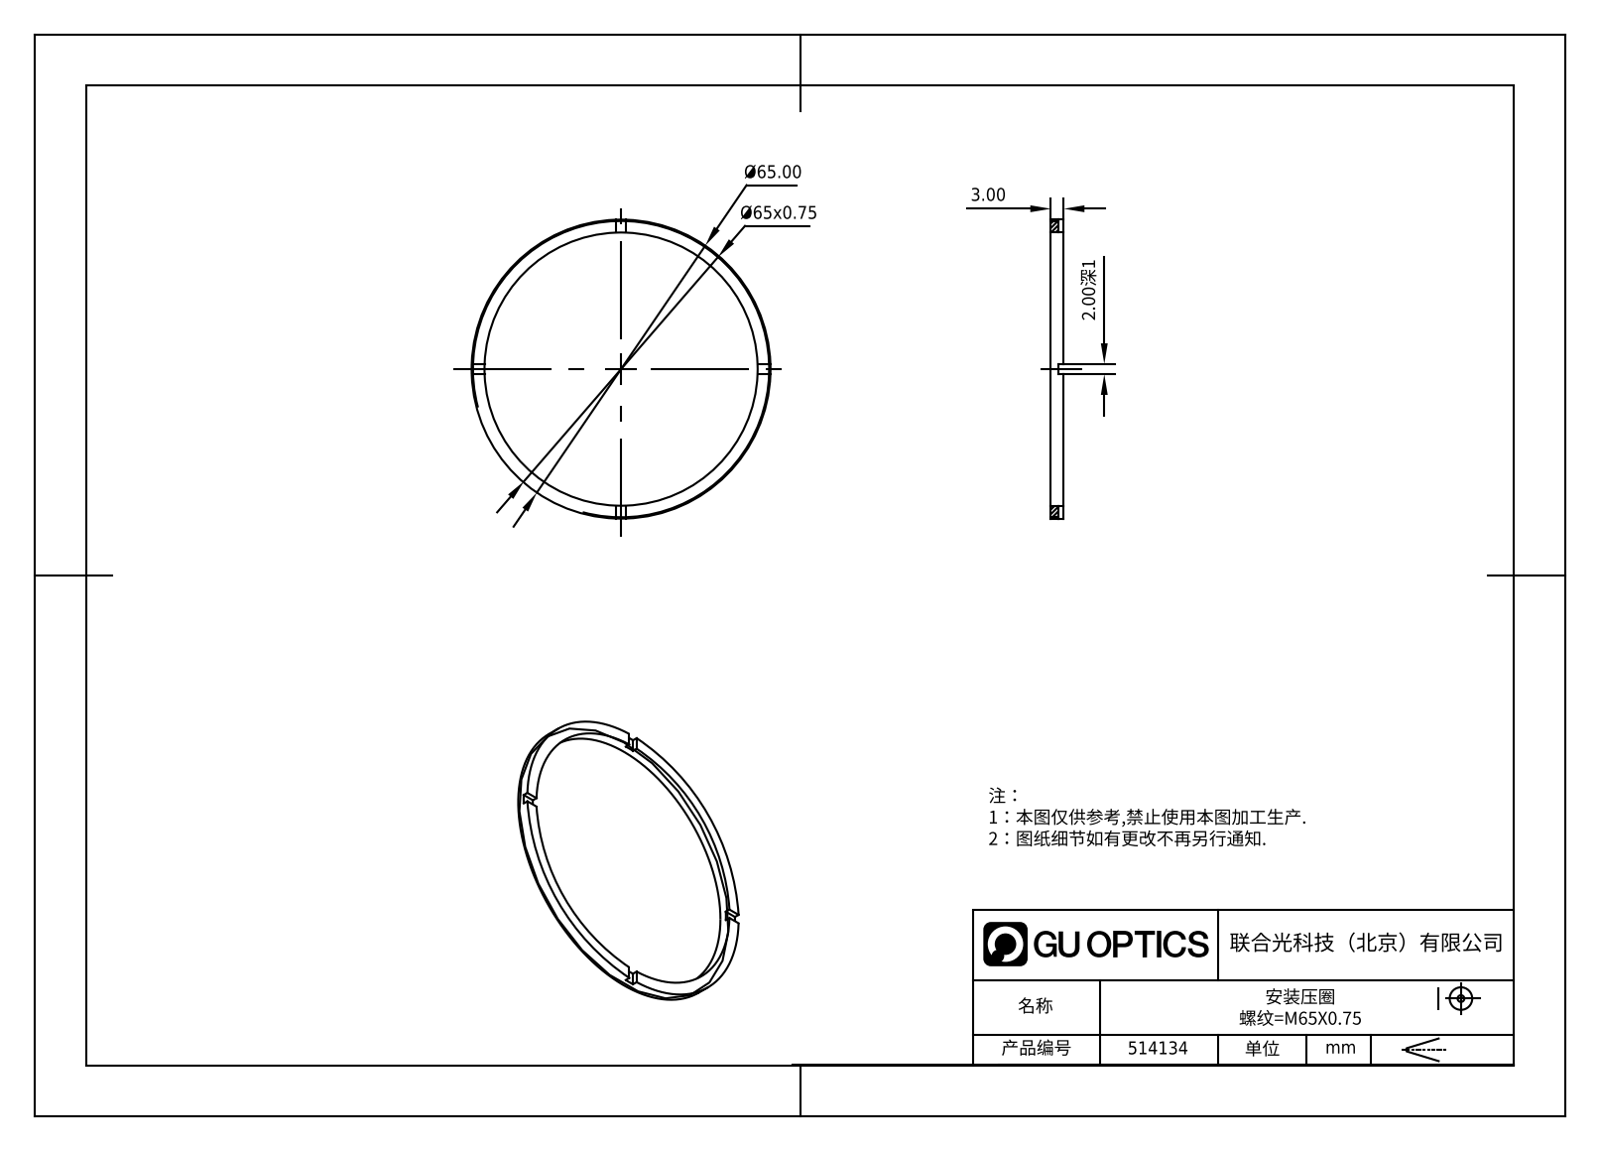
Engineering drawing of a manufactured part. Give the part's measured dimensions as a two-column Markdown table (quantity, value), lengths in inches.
| quantity | value |
| --- | --- |
| part name | 514134 |
| STEP written by | SolidWorks 2020 (CONFIG_CONTROL_DESIGN) |
| units | inches |
| bodies | 1 solid, 21 faces (17 planar, 4 cylindrical, 0 other) |
| overall size | 2.559 × 2.559 × 0.118 |
| volume | 0.089 in³ |
| surface area | 3.354 in² |
| round holes (diameter × count) | 2.362 × 1 |
| round bosses / shafts (diameter × count) | 2.559 × 1 |
| main face-to-face distances | 0.118, 0.079, 0.039 |
